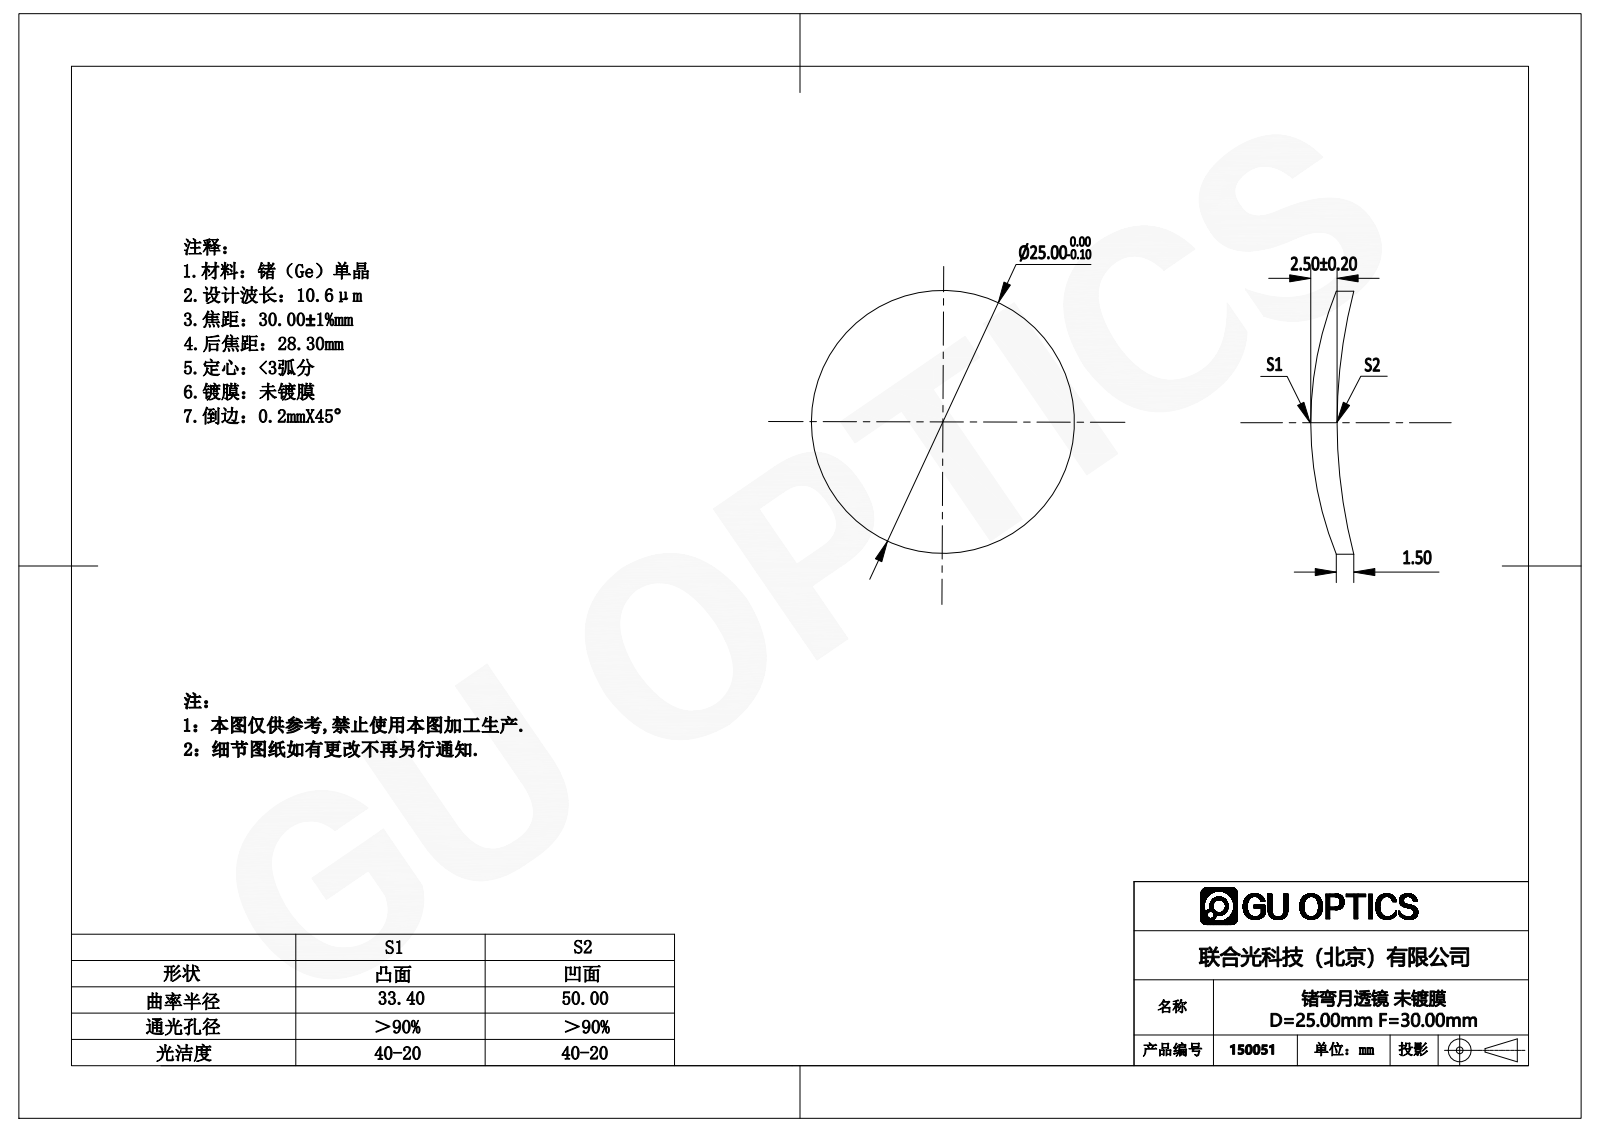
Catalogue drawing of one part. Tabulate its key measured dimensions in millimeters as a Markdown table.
| quantity | value |
| --- | --- |
| part name | 150051 |
| STEP written by | SolidWorks 2016 (AUTOMOTIVE_DESIGN) |
| units | millimeters |
| bodies | 1 solid, 6 faces (0 planar, 2 cylindrical, 4 other) |
| overall size | 25 × 25 × 4.09 |
| volume | 1 027 mm³ |
| surface area | 1 139 mm² |
| round bosses / shafts (diameter × count) | 25 × 1 |
